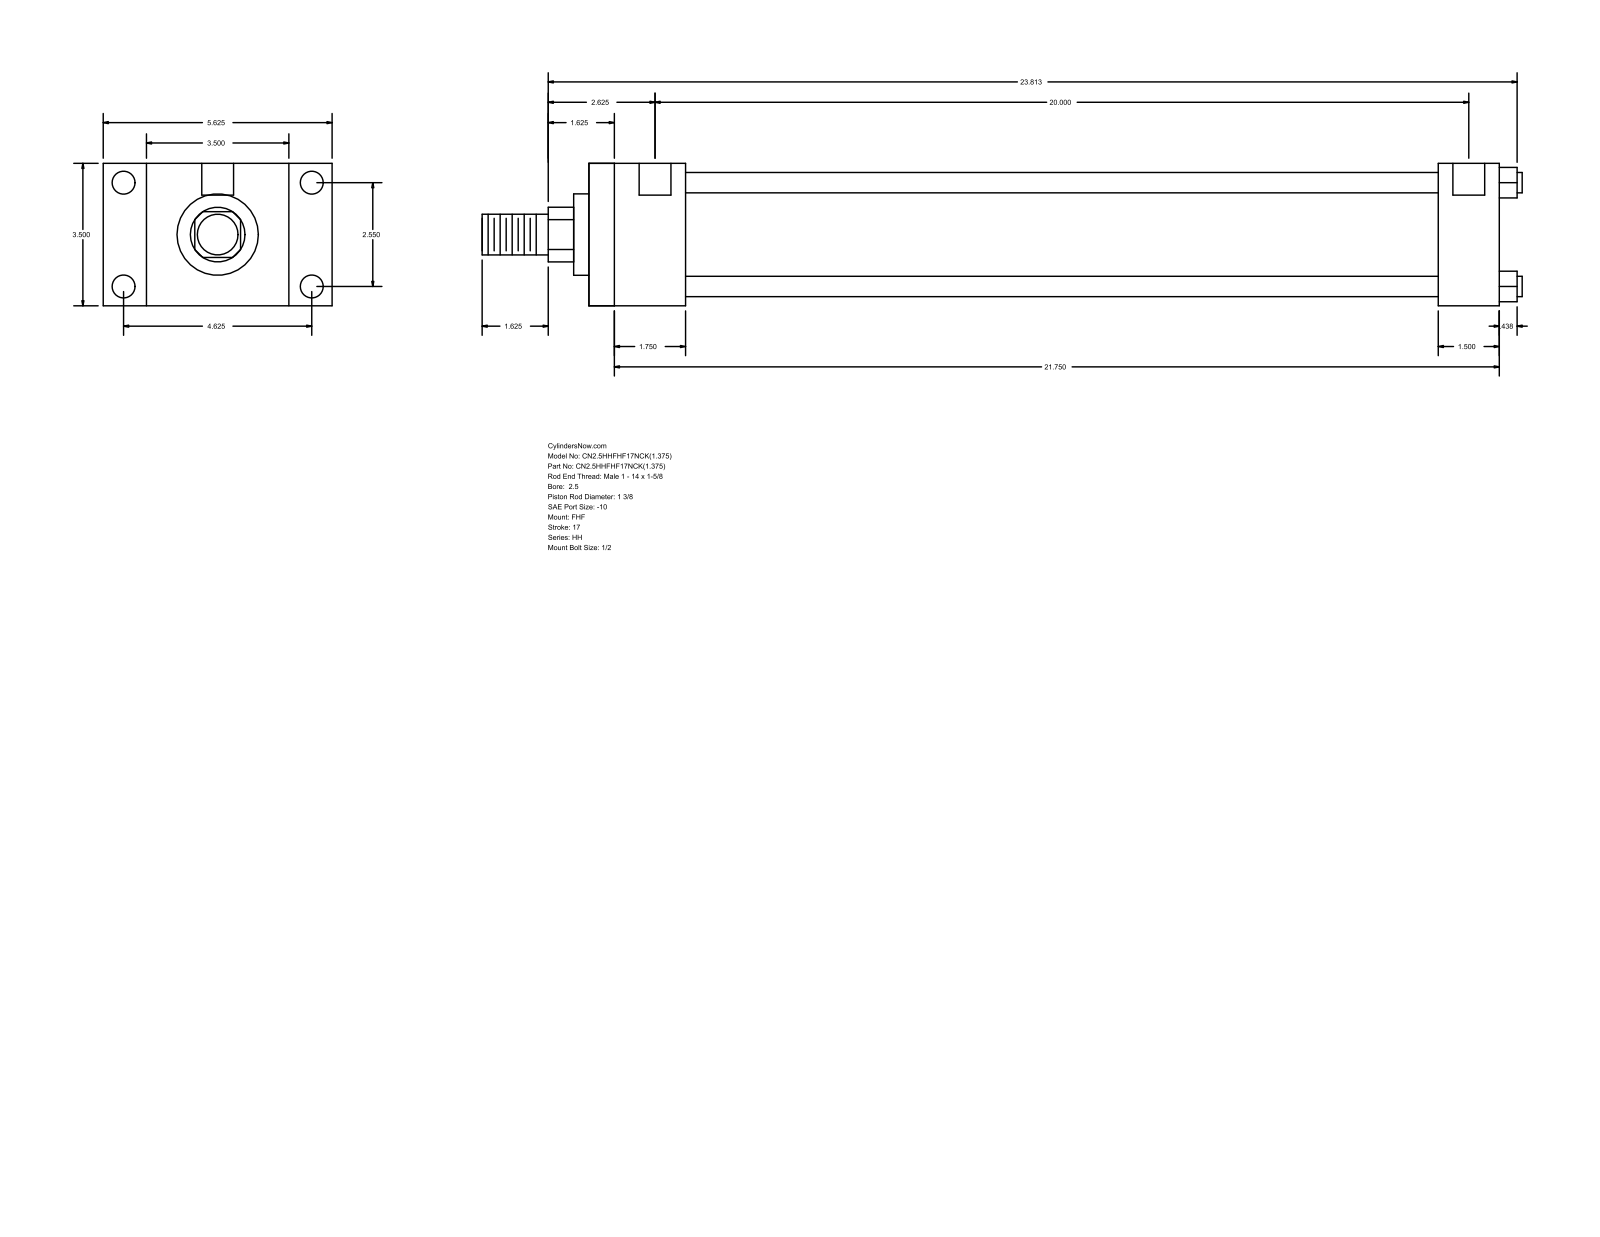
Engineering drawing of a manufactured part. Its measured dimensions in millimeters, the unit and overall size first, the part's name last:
Units: millimetres
Overall size (bounding box): 649.29 × 142.88 × 88.9
Round holes (diameter × count): ⌀5.56 ×4, ⌀14.3 ×4, ⌀19.84 ×2
Round bosses / shafts (diameter × count): ⌀12.7 ×4, ⌀73.03 ×1, ⌀50.8 ×1, ⌀34.92 ×1, ⌀25.4 ×1
Partial cylindrical surfaces — rounded edges, fillets, slot ends (radius × count): R17.06 ×1
Main face-to-face distances: 88.9, 60.32, 26.99, 115.89, 568.33, 508.01, 142.88, 530.22, 469.9, 38.11
Hole centre spacings: 64.76, 117.48, 134.15, 511.17, 1.58, 1.59, 508, 509.58
Bodies: 0 solids, 88 faces (60 planar, 28 cylindrical, 0 other)
Part name (STEP PRODUCT): HH_FHF__0250_1.375
STEP written by: GSSL Pune (CONFIG_CONTROL_DESIGN)
